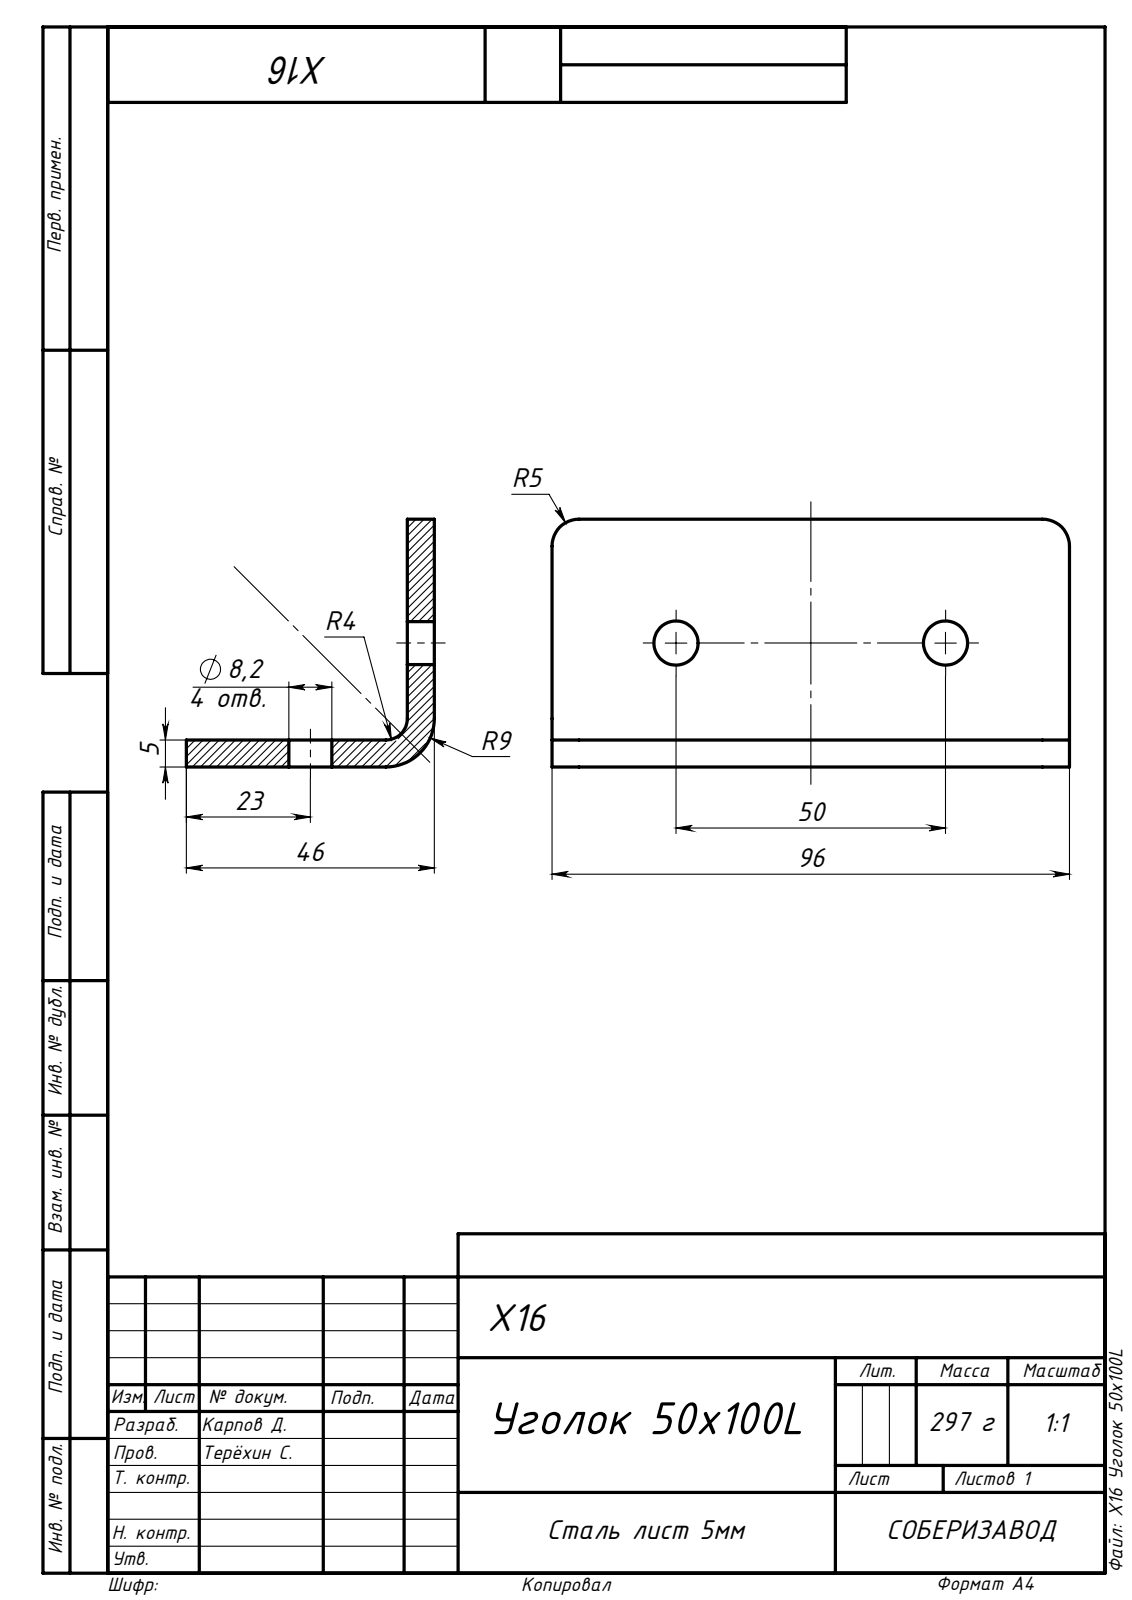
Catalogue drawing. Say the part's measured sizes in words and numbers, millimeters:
Its 3-D file was written by "SolidWorks 2021 (AUTOMOTIVE_DESIGN)". It is 1 solid with 26 faces: 12 planar, 14 cylindrical and 0 other. Overall it measures 96 by 46 by 46 millimeters. Its volume is 39 257 cubic millimeters and its surface area 17 977 square millimeters. Round holes: 4 of diameter 8.2. Partial cylindrical surfaces (rounded edges, fillets, slot ends): 4 of radius 5, 1 of radius 4, 1 of radius 9. The main face-to-face distances are 5, 46, 41, 96. The hole center spacings are 50.
